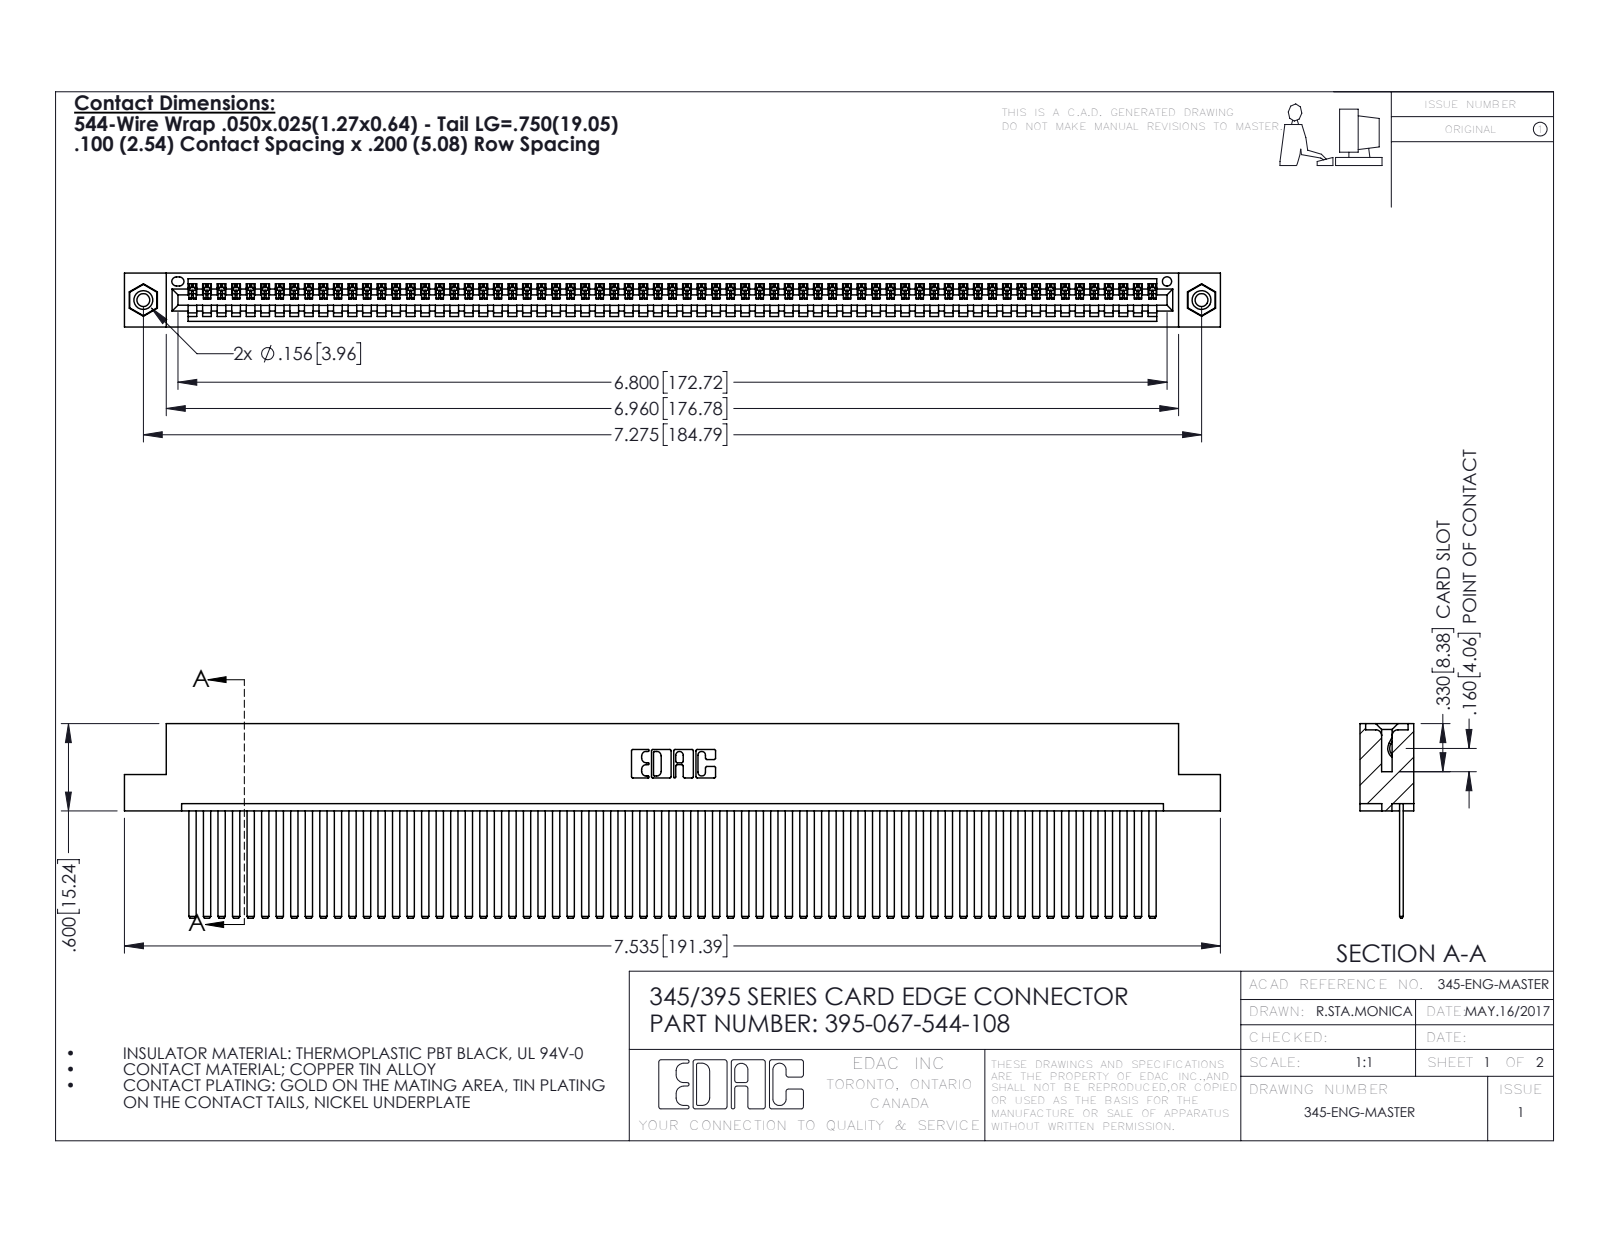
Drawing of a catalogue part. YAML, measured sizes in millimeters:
part_name: "345 Part_Flush Mounting Lugs - 0.156 Dia-TI; 395-067-544-108; 345-250-001_345-250-003-102; 345-292-001_345-293-144"
step_written_by: "SolidWorks 2016 (CONFIG_CONTROL_DESIGN)"
units: millimeters
bodies: {solids: 70, faces: 3670, planar: 2524, cylindrical: 1130, other: 16}
overall_size: [191.4, 34, 9.4]
volume: 19160
surface_area: 28140
round_holes:
  - {diameter: 2.3, count: 2}
  - {diameter: 3.2, count: 2}
  - {diameter: 4, count: 2}
  - {diameter: 1.6, count: 1}
round_bosses_or_shafts:
  - {diameter: 3.9, count: 2}
partial_cylinders:
  - {radius: 0.2, count: 134}
  - {radius: 0.3, count: 22}
  - {radius: 0.2, count: 6}
  - {radius: 0.8, count: 6}
  - {radius: 0.7, count: 3}
  - {radius: 0.8, count: 2}
  - {radius: 1, count: 2}
  - {radius: 0.4, count: 1}
face_to_face_distances: [1.8, 7.6, 0.6, 2.5, 6.9, 9.4, 5.1, 5.7, 3.8, 1.8]
hole_center_spacings: [6.9, 178.8, 184.8]
